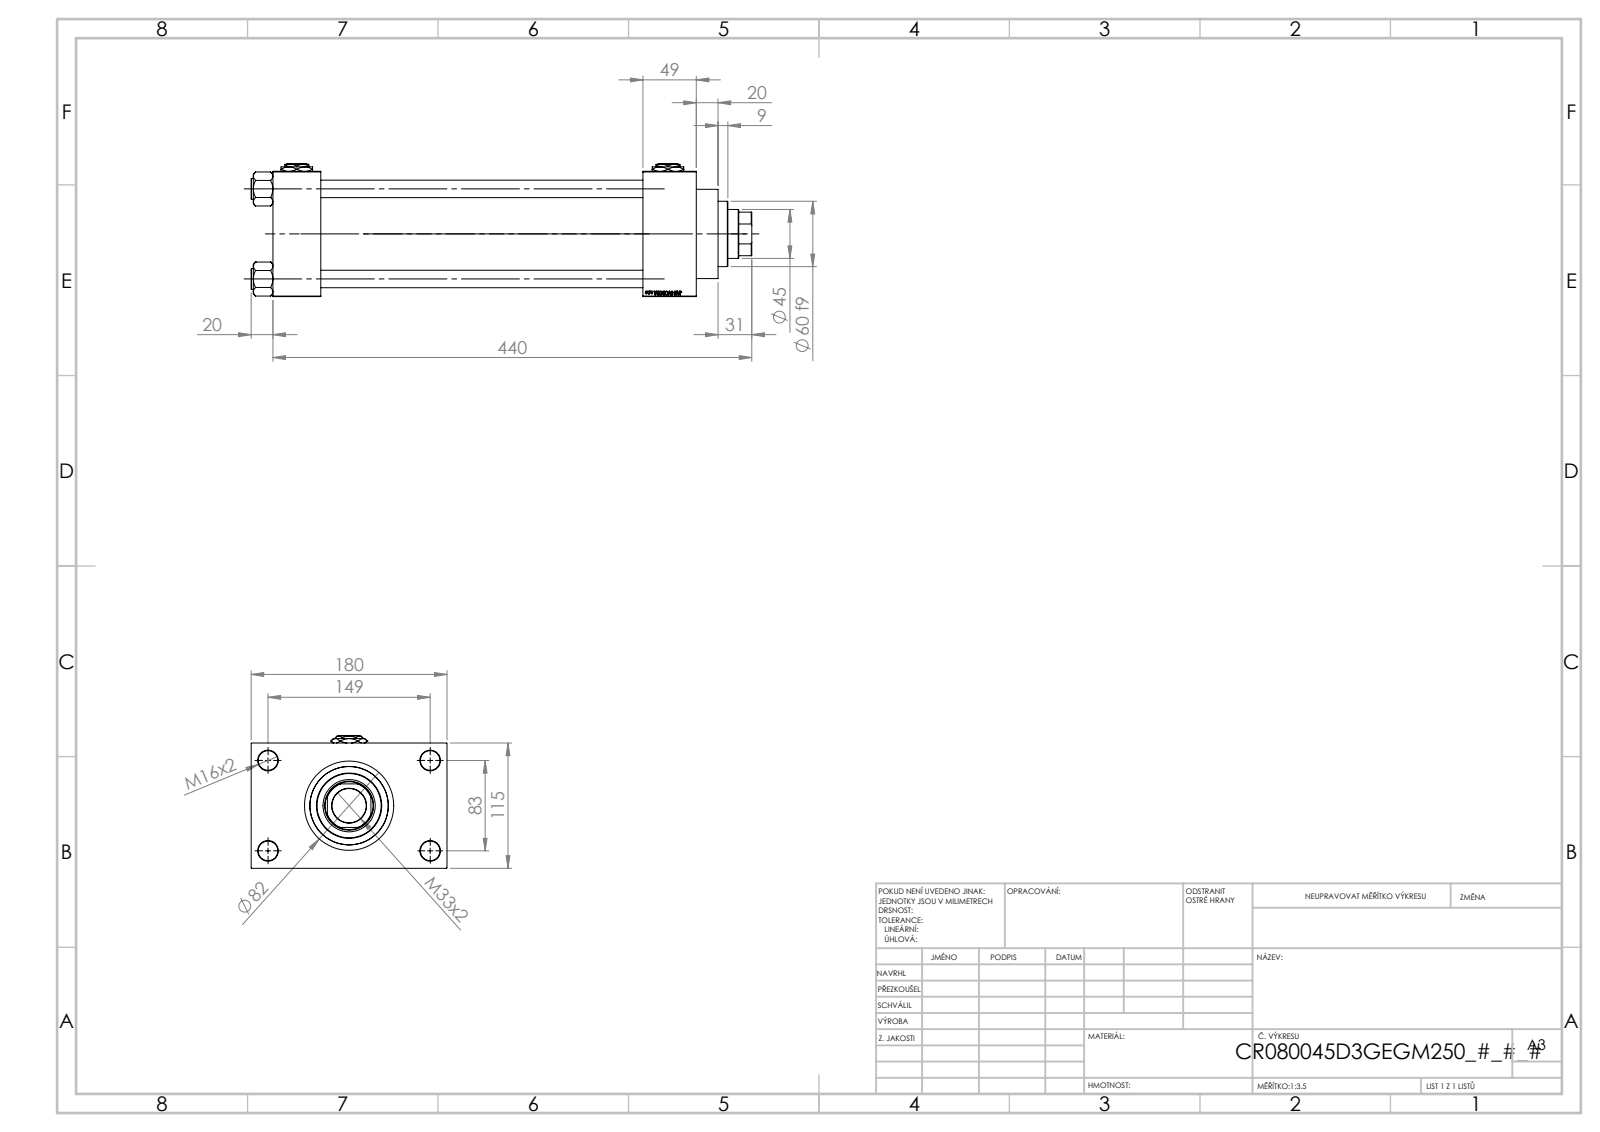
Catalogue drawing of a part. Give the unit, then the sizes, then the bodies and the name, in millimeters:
Units: millimetres
Overall size (bounding box): 460 × 180 × 122
Round holes (diameter × count): ⌀16 ×4, ⌀18 ×4, ⌀7 ×2, ⌀26.44 ×2, ⌀35 ×2, ⌀31.5 ×1, ⌀45 ×1, ⌀48 ×1, ⌀61 ×1, ⌀72 ×1, ⌀80 ×1
Round bosses / shafts (diameter × count): ⌀19 ×4, ⌀86 ×1, ⌀82 ×1, ⌀60 ×1
Partial cylindrical surfaces — rounded edges, fillets, slot ends (radius × count): R22 ×1
Main face-to-face distances: 115, 296, 345, 49, 44, 340, 389, 32.5, 147.5, 180
Hole centre spacings: 33.15, 58.48, 82.7, 85.28, 89.24, 115.85, 142.43, 83
Volume: 2 739 000 mm³ · Surface area: 505 174 mm²
Bodies: 13 solids, 1253 faces (593 planar, 100 cylindrical, 560 other)
Part name (STEP PRODUCT): Zatka_pro_OIL_PORT; V215CR_VCP_D; NUT_M5_D; V215_VC_A (+2 more)
STEP written by: SolidWorks 2019 (CONFIG_CONTROL_DESIGN)
